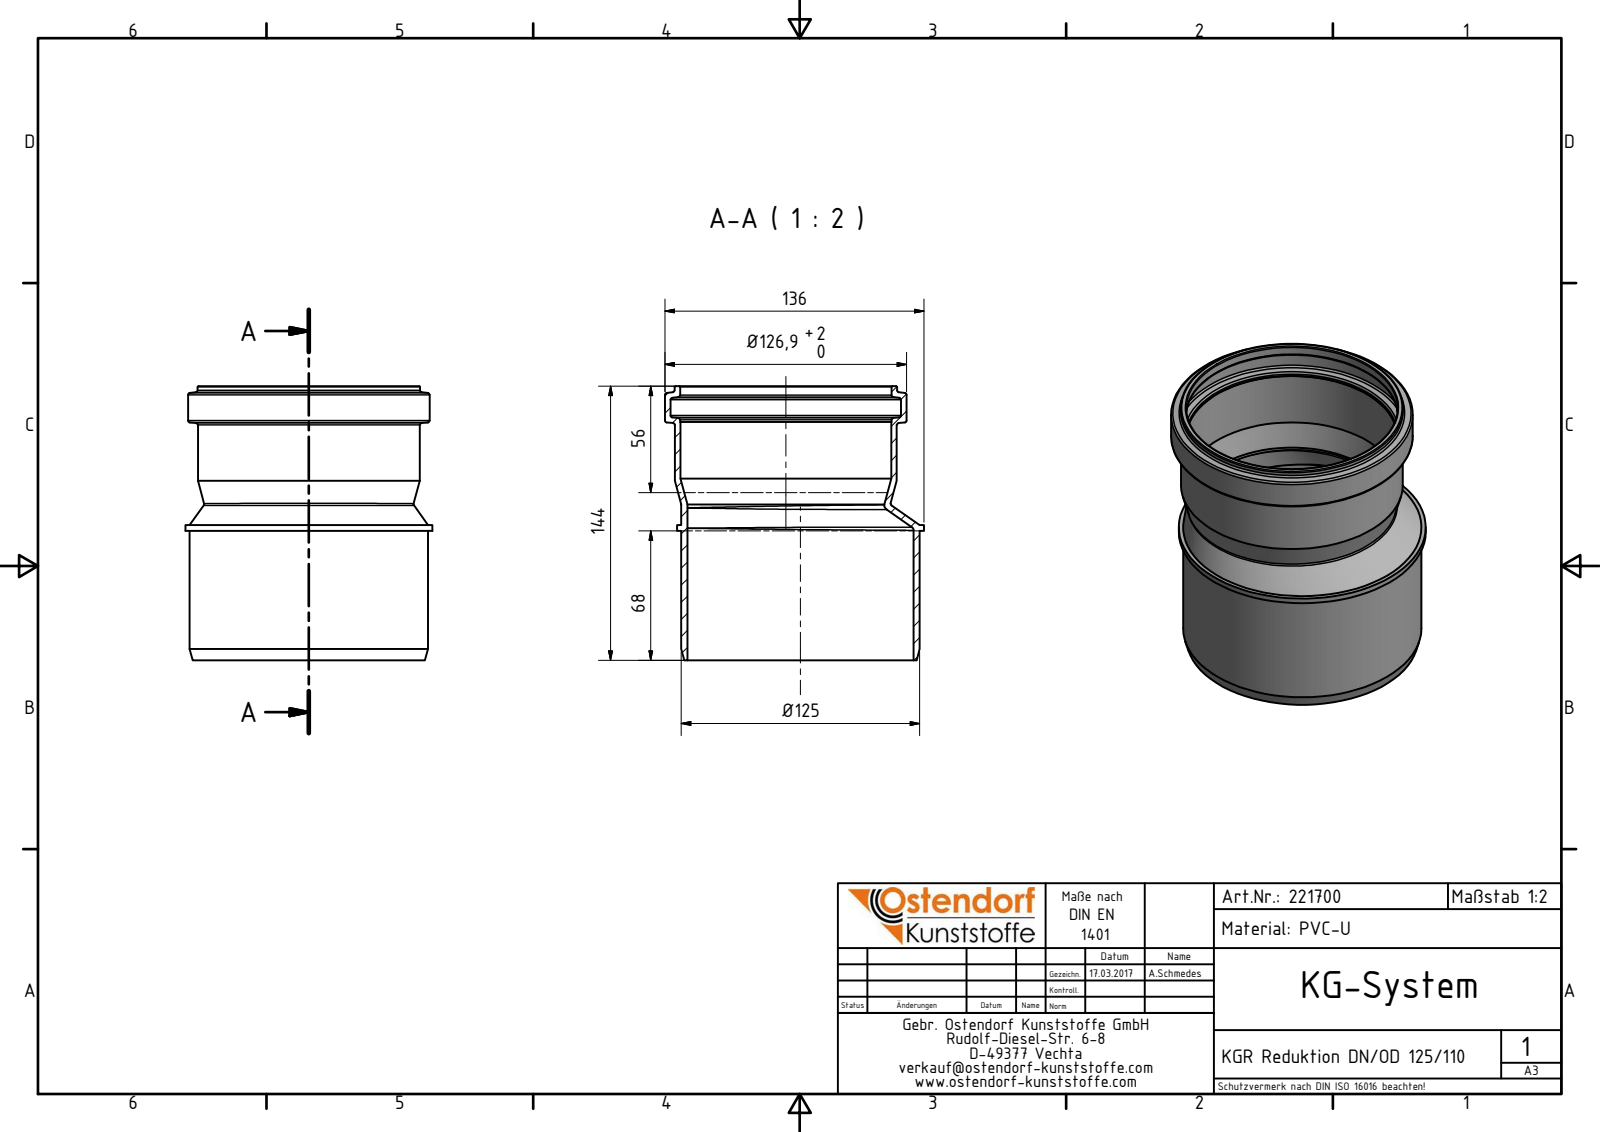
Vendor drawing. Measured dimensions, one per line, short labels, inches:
name: 221700 KGR Reduktion DN_OD 125_110
written by: Autodesk Inventor 2016 (AUTOMOTIVE_DESIGN)
unit: in
bodies: 1 solid, 38 faces (5 planar, 11 cylindrical, 22 other)
size: 5.669 × 5.354 × 5.106
volume: 11.06 in³; area: 184.3 in²
holes: 1× ⌀4.071, 1× ⌀4.358, 1× ⌀4.37, 1× ⌀4.677, 1× ⌀4.768
bosses: 1× ⌀5.106, 1× ⌀4.996, 1× ⌀4.929, 1× ⌀4.598, 1× ⌀4.587
face distances: 0.118, 2.992, 2.874, 2.677, 2.795, 5.669, 4.928, 2.251, 2.133, 0.741
hole spacings: 0.303
